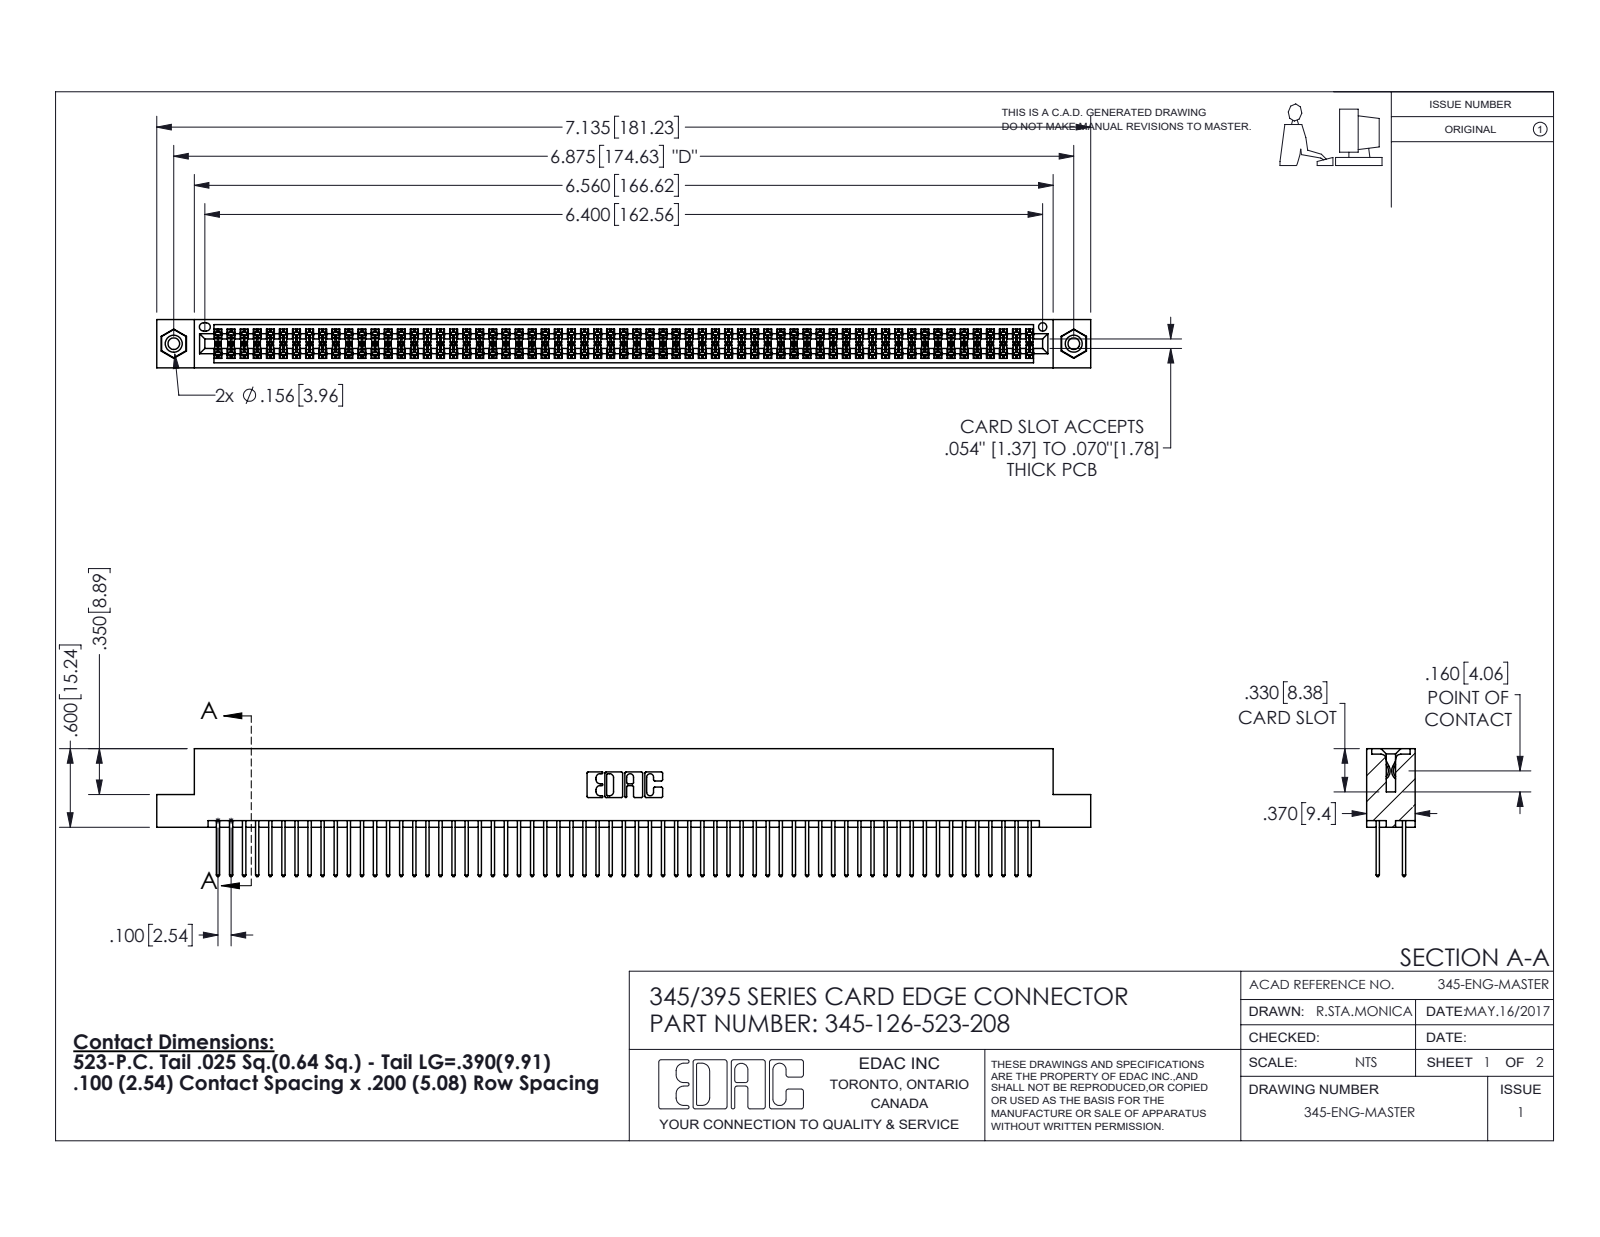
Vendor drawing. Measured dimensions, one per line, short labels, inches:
name: 345-292-001_345-293-123; 345-250-001_345-250-003-102; 345-126-523-208; 345 Part_Flush Mounting Lugs - 0.156 Dia-TI
written by: SolidWorks 2016 (CONFIG_CONTROL_DESIGN)
unit: in
bodies: 129 solids, 6486 faces (4270 planar, 2200 cylindrical, 16 other)
size: 7.135 × 0.977 × 0.37
volume: 1.102 in³; area: 43.81 in²
holes: 2× ⌀0.089, 2× ⌀0.125, 2× ⌀0.156, 1× ⌀0.064
bosses: 2× ⌀0.155
rounds: 189× R0.006, 126× R0.01, 22× R0.01, 6× R0.007, 6× R0.031, 3× R0.026, 2× R0.014, 2× R0.019
face distances: 0.072, 0.298, 0.2, 0.098, 0.272, 0.025, 0.37, 0.225, 0.175, 0.149
hole spacings: 0.27, 6.639, 6.875
